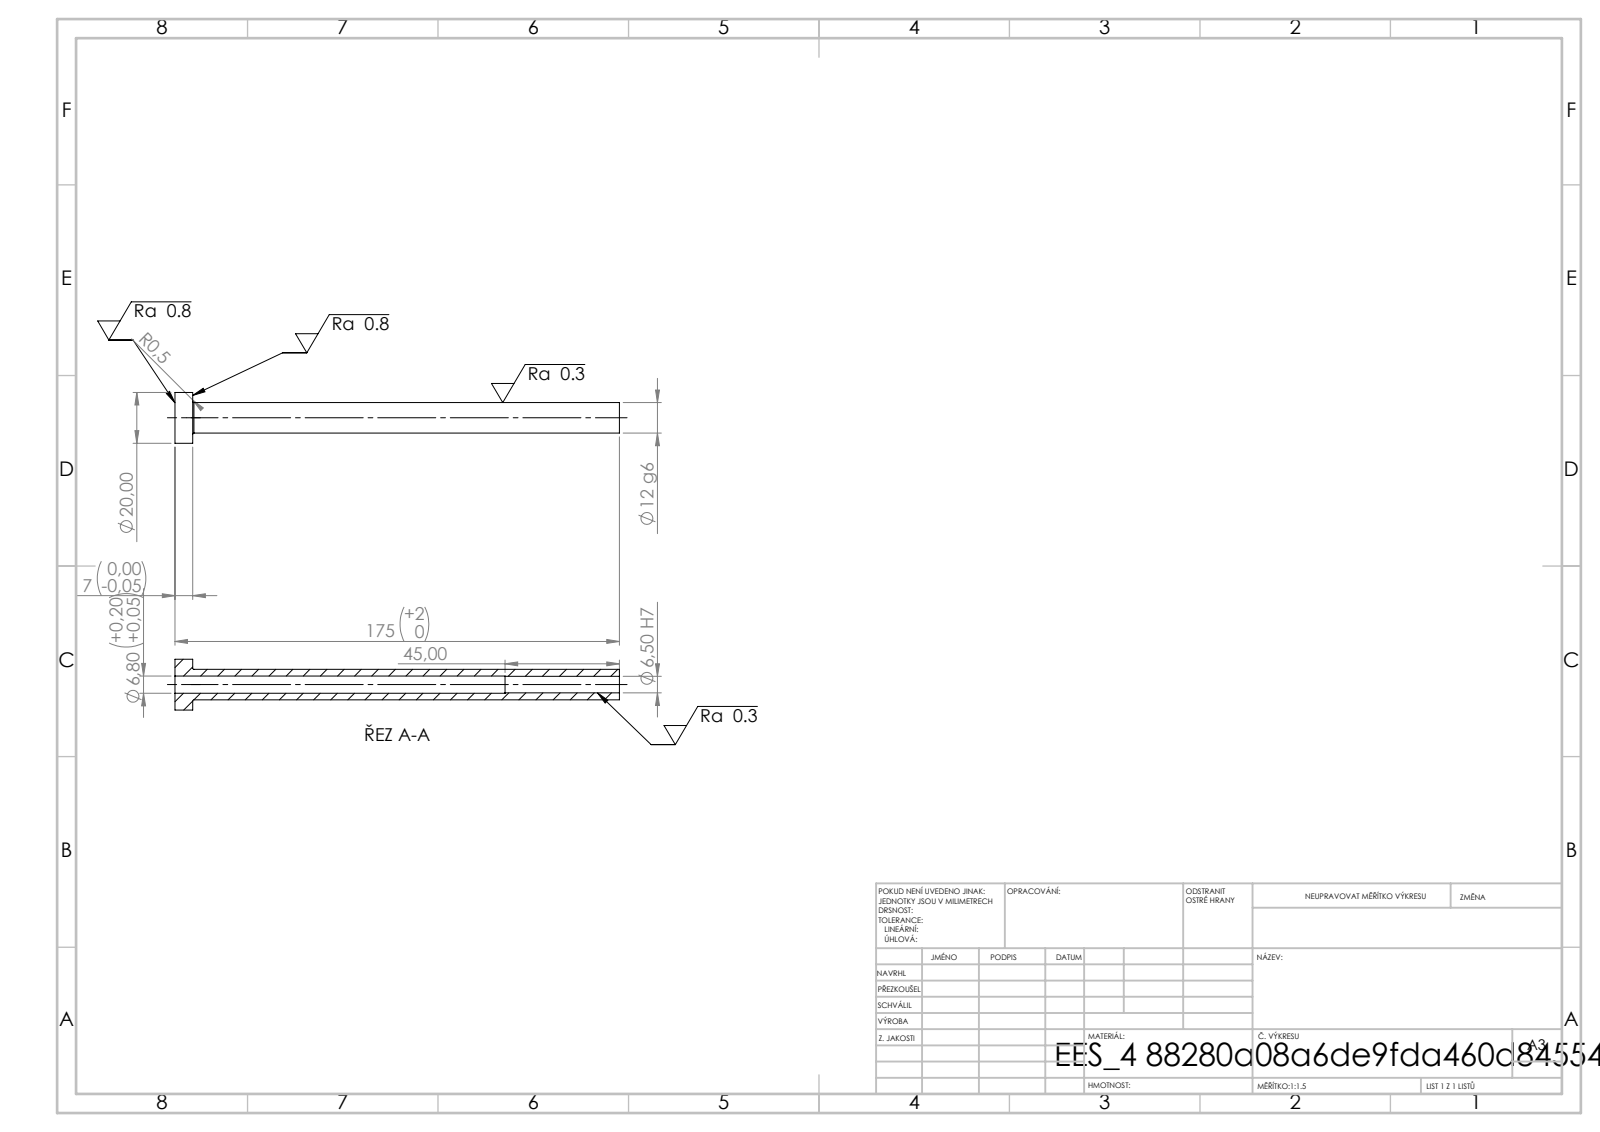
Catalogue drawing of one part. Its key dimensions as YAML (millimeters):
step_written_by: "SolidWorks 2019 (CONFIG_CONTROL_DESIGN)"
units: millimeters
bodies: {solids: 1, faces: 14, planar: 4, cylindrical: 8, other: 2}
overall_size: [175, 20, 20]
volume: 14987
surface_area: 11023
round_holes:
  - {diameter: 6.5, count: 1}
  - {diameter: 6.8, count: 1}
round_bosses_or_shafts:
  - {diameter: 20, count: 1}
  - {diameter: 12, count: 1}
face_to_face_distances: [7, 175, 168, 130, 123, 45]
